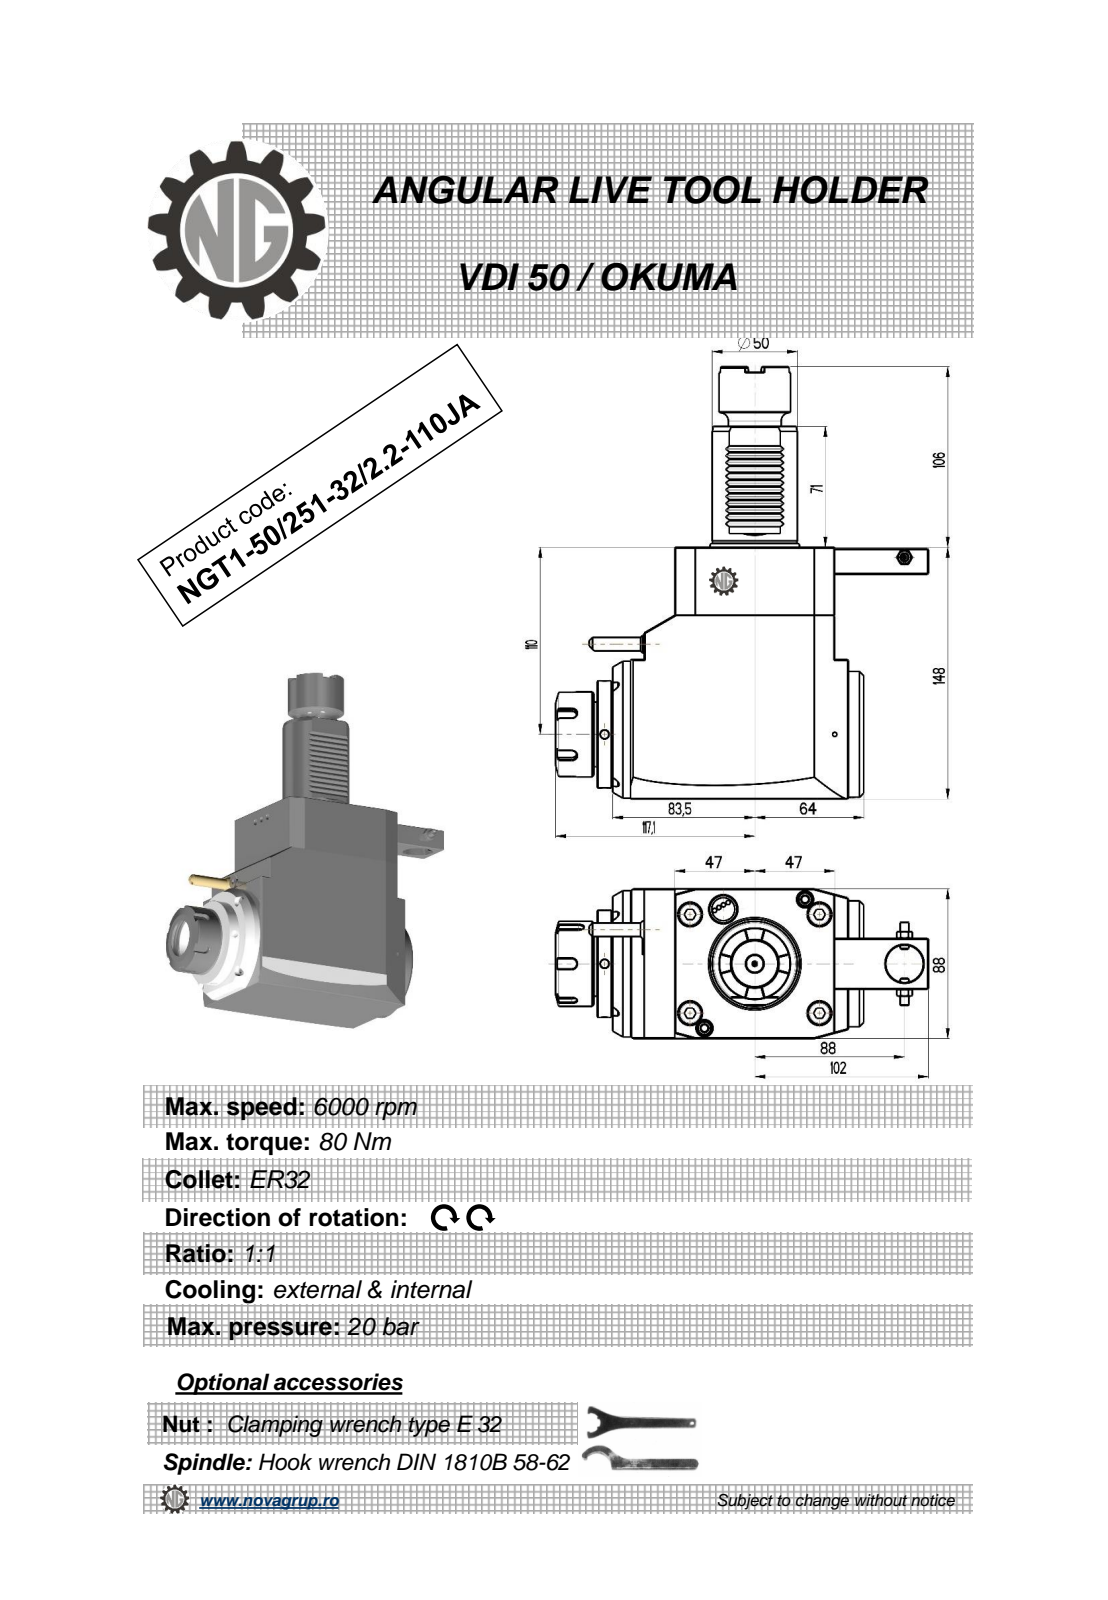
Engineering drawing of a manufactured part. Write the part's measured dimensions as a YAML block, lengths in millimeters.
part_name: "NGT1_50_251_32_1_2_110JA"
step_written_by: "PRO/ENGINEER BY PARAMETRIC TECHNOLOGY CORPORATION, 2010280 (CONFIG_CONTROL_DESIGN)"
units: millimeters
bodies: {solids: 1, faces: 460, planar: 209, cylindrical: 93, other: 158}
overall_size: [254, 219.1, 88]
volume: 1840000
surface_area: 118458
round_holes:
  - {diameter: 5, count: 3}
  - {diameter: 3, count: 1}
  - {diameter: 4.5, count: 1}
  - {diameter: 9.5, count: 1}
  - {diameter: 22, count: 1}
  - {diameter: 27, count: 1}
  - {diameter: 28, count: 1}
round_bosses_or_shafts:
  - {diameter: 50, count: 2}
  - {diameter: 86, count: 1}
  - {diameter: 74, count: 1}
  - {diameter: 63, count: 1}
  - {diameter: 50.5, count: 1}
  - {diameter: 42, count: 1}
  - {diameter: 41, count: 1}
  - {diameter: 31, count: 1}
partial_cylinders:
  - {radius: 0.26, count: 12}
  - {radius: 0.3, count: 12}
  - {radius: 0.2, count: 6}
  - {radius: 3, count: 5}
  - {radius: 2.5, count: 1}
face_to_face_distances: [88, 148, 147.5, 9, 17, 8, 111, 94, 36.5, 130.5]
hole_center_spacings: [52.46, 56.65, 88, 88.25, 101.5, 176.25]
